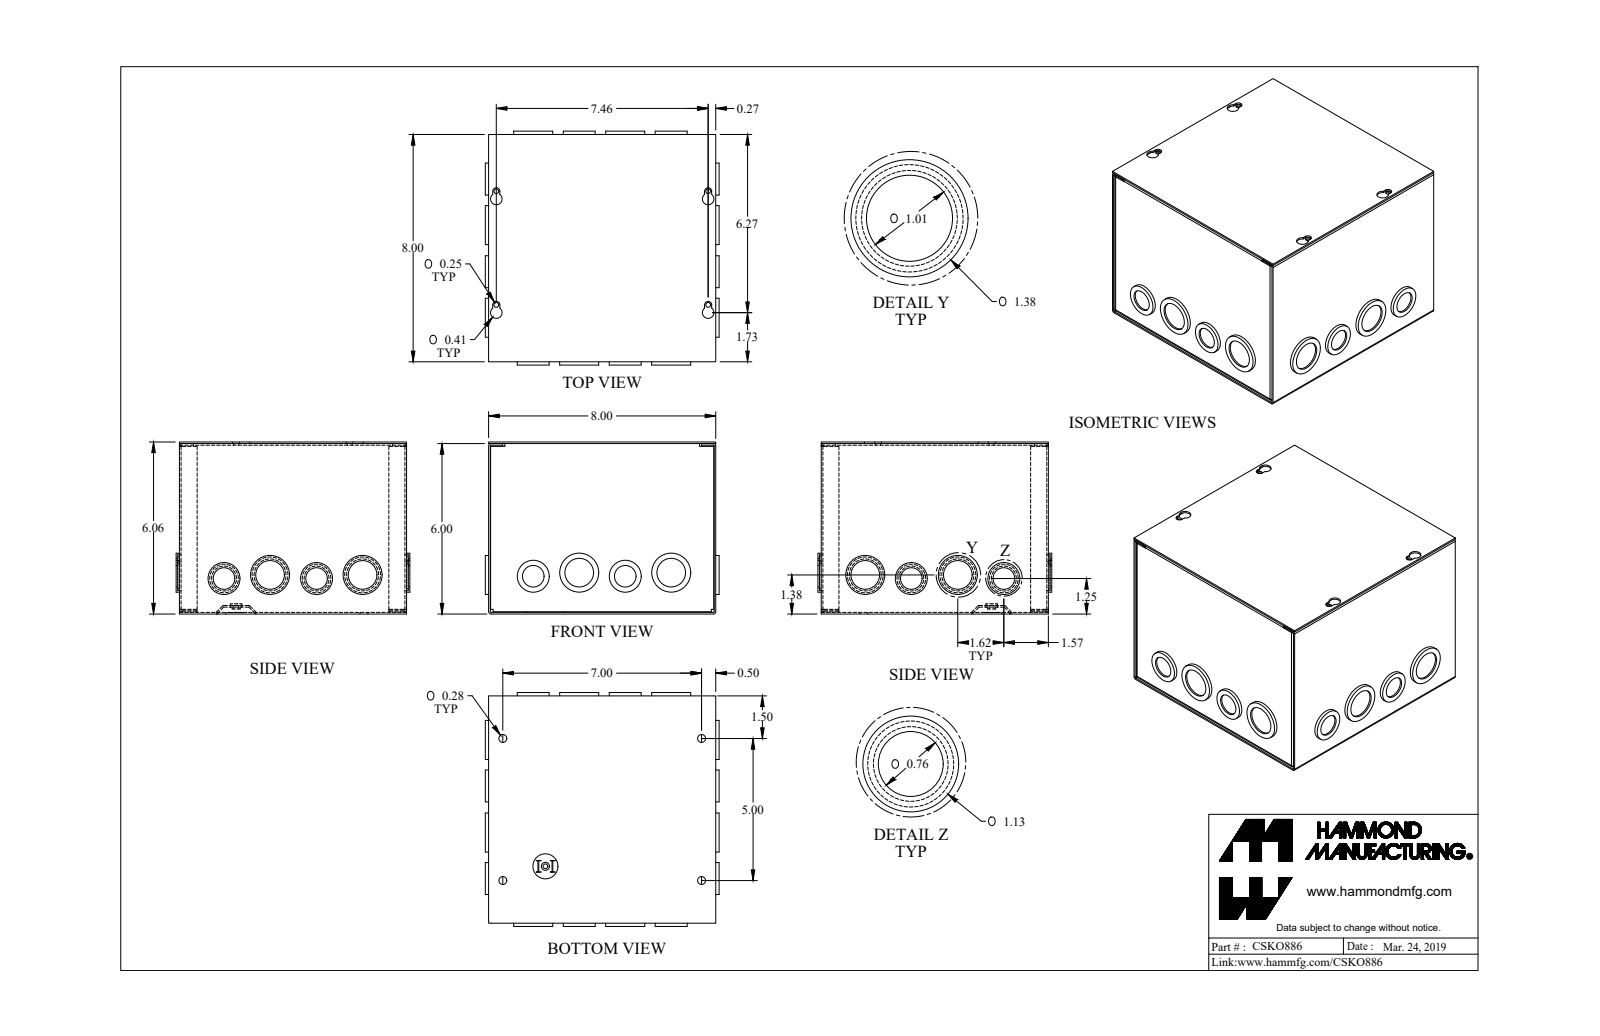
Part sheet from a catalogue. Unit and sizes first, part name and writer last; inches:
Units: inches
Overall size (bounding box): 8.234 × 8.234 × 6.057
Round holes (diameter × count): ⌀1.011 ×12, ⌀0.761 ×6, ⌀1.261 ×6, ⌀0.17 ×5, ⌀0.281 ×4, ⌀0.5 ×1
Round bosses / shafts (diameter × count): ⌀1.125 ×7, ⌀1.375 ×6, ⌀1.125 ×6, ⌀0.875 ×5, ⌀0.875 ×3, ⌀0.492 ×1, ⌀0.284 ×1
Partial cylindrical surfaces — rounded edges, fillets, slot ends (radius × count): R0.029 ×12, R0.086 ×12, R0.057 ×8, R0.125 ×4, R0.203 ×4
Main face-to-face distances: 0.057, 7.943, 6, 8, 7.886, 5.943, 6.057, 7.873, 0.07, 0.114
Hole centre spacings: 1.625, 0.125, 0.55, 1.62, 3.24, 3.242, 4.506, 7.247
Volume: 20.41 in³ · Surface area: 725.6 in²
Bodies: 4 solids, 397 faces (189 planar, 200 cylindrical, 8 other)
Part name (STEP PRODUCT): CSKO886_Default
STEP written by: SolidWorks 2019 (CONFIG_CONTROL_DESIGN)
